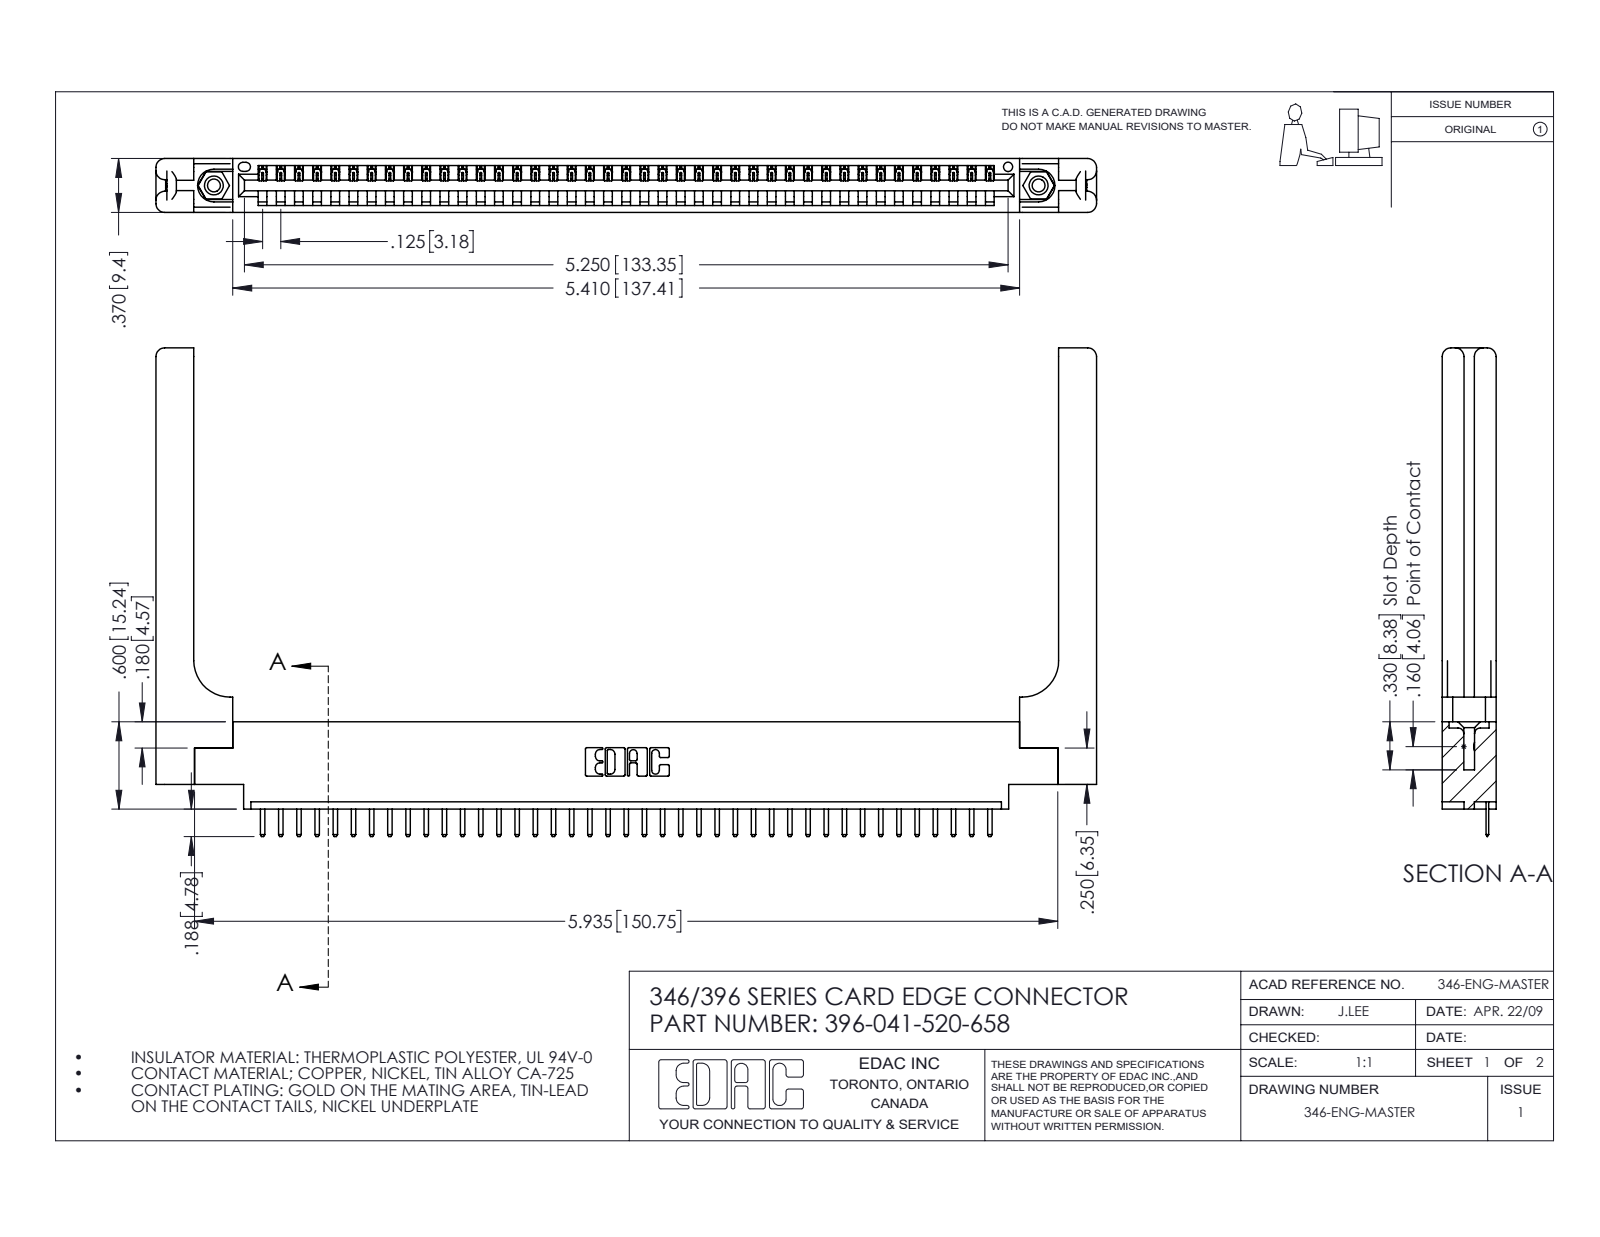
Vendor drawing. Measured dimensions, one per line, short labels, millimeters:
name: 396-041-520-658; 345-292-001_345-293-120; 345-250-001_345-250-001-102; 346-220-058_345-220-058 (+1 more)
written by: SolidWorks 2016 (CONFIG_CONTROL_DESIGN)
unit: mm
bodies: 46 solids, 2924 faces (1950 planar, 914 cylindrical, 60 other)
size: 164.2 × 85.3 × 9.4
volume: 22 960 mm³; area: 24 230 mm²
holes: 2× ⌀2.3, 2× ⌀3.2, 2× ⌀4, 1× ⌀1.6
bosses: 2× ⌀3.9
rounds: 84× R0.3, 82× R0.2, 22× R0.3, 16× R1.5, 6× R0.2, 6× R0.8, 3× R0.7, 2× R0.8
face distances: 9.4, 1.2, 8.2, 1.8, 3.8, 3.8, 6.4, 7.6, 0.6, 5.6
hole spacings: 6.2, 138.7, 144
